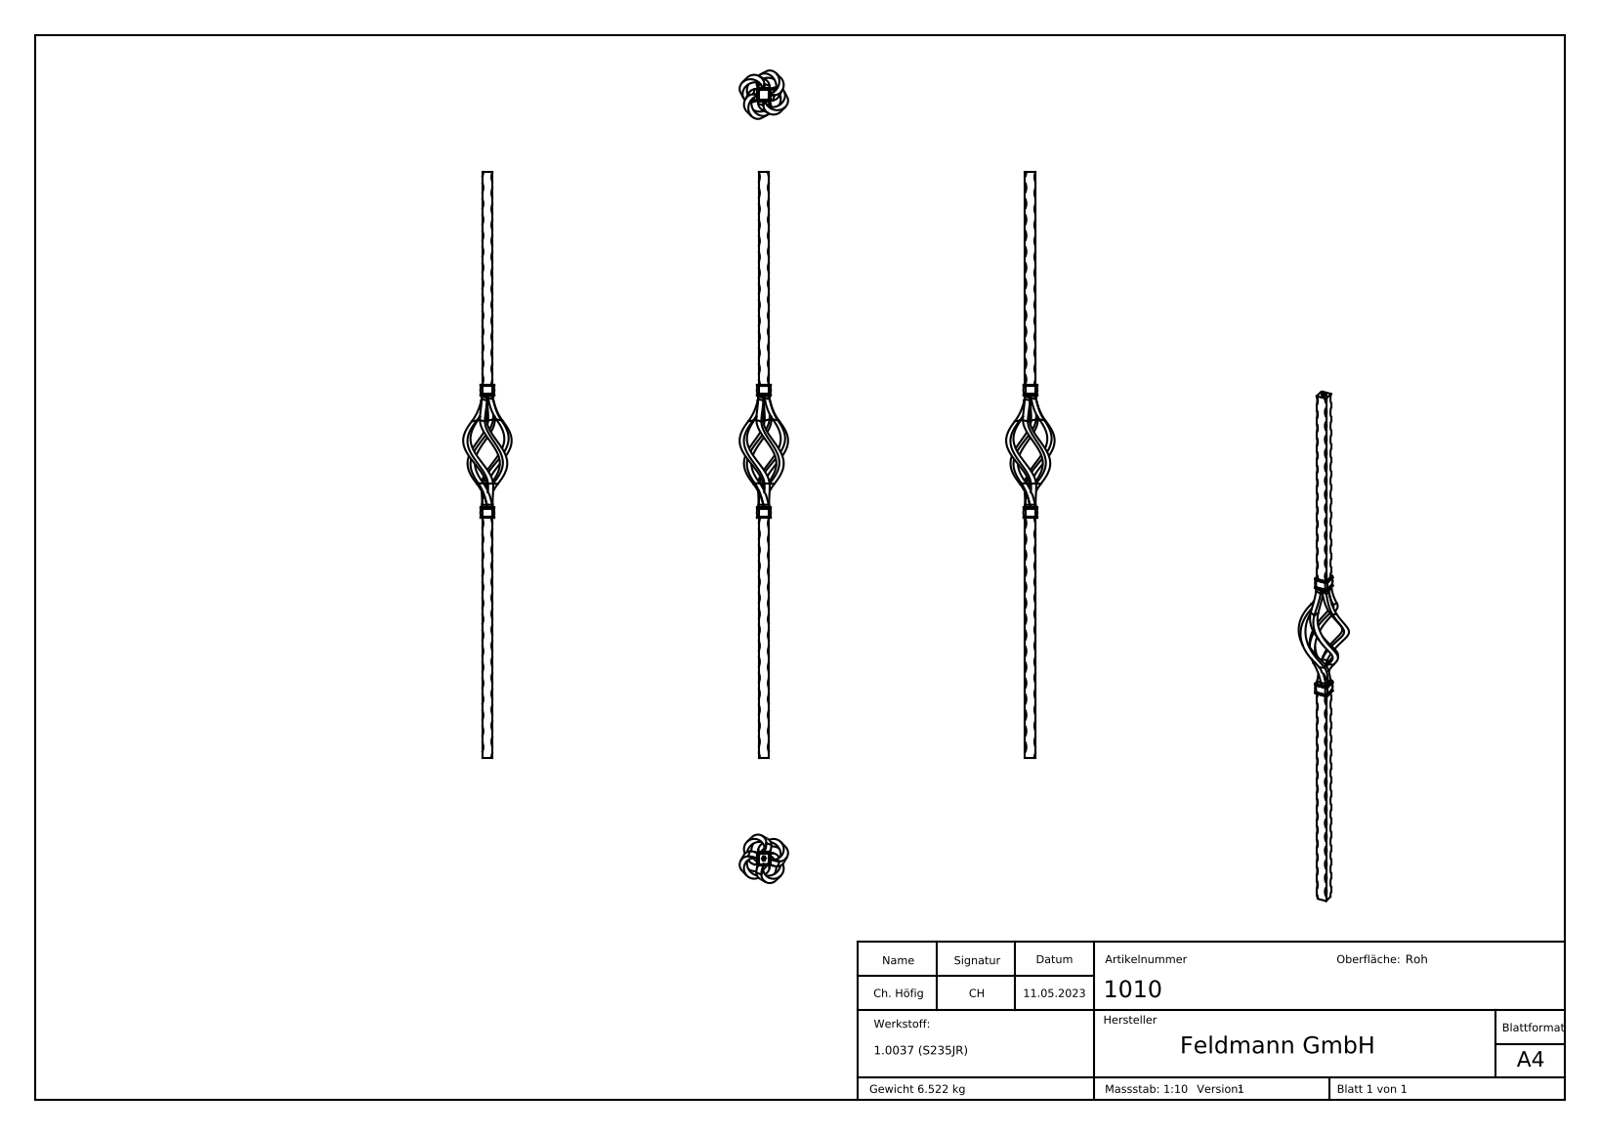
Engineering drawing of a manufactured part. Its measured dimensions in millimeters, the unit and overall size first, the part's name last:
Units: millimetres
Overall size (bounding box): 1100 × 90.84 × 90.84
Round bosses / shafts (diameter × count): ⌀20 ×1
Partial cylindrical surfaces — rounded edges, fillets, slot ends (radius × count): R0.5 ×68, R19 ×8, R3.5 ×4
Main face-to-face distances: 20, 20.2, 20.4, 210, 230, 470, 680, 1100, 630, 420
Volume: 836 113 mm³ · Surface area: 144 295 mm²
Bodies: 4 solids, 715 faces (241 planar, 116 cylindrical, 358 other)
Part name (STEP PRODUCT): 1010
STEP written by: SolidWorks 2018 (CONFIG_CONTROL_DESIGN)
